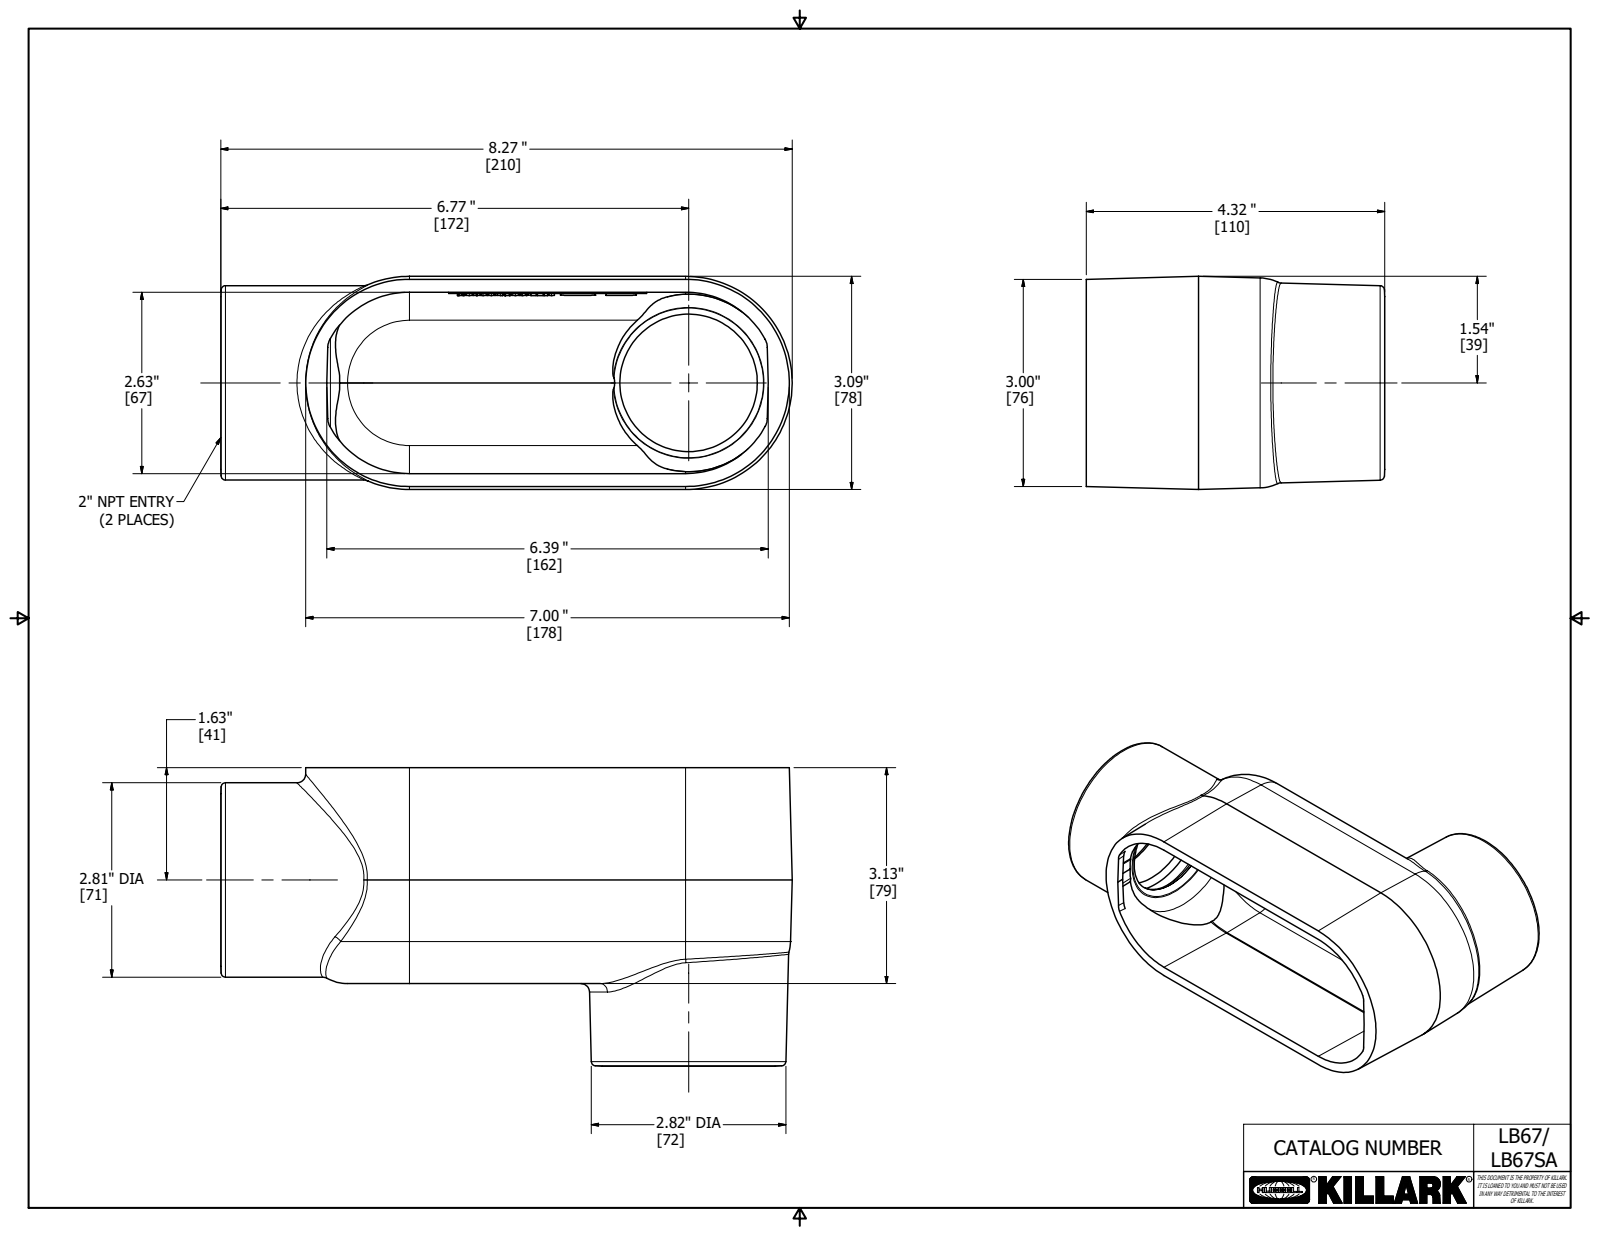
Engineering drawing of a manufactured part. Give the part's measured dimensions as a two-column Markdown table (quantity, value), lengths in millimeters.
| quantity | value |
| --- | --- |
| part name | 17708-2 |
| STEP written by | Autodesk Inventor 2018 (AUTOMOTIVE_DESIGN) |
| units | millimeters |
| bodies | 1 solid, 879 faces (531 planar, 33 cylindrical, 315 other) |
| overall size | 210.2 × 109.8 × 78.4 |
| volume | 279 100 mm³ |
| surface area | 108 500 mm² |
| round holes (diameter × count) | 60.5 × 2, 1.2 × 1, 10.3 × 1, 65.9 × 1 |
| round bosses / shafts (diameter × count) | 71.5 × 1, 12.7 × 1, 1.4 × 1 |
| partial cylindrical surfaces (radius × count) | 3.2 × 4, 11.1 × 2, 12.7 × 2, 15.9 × 2, 0.2 × 1, 0.2 × 1, 0.4 × 1, 1.6 × 1 |
| main face-to-face distances | 4.7, 73.6, 78.4, 68.8, 79.4, 5.6, 72.8, 68, 0.8, 0.8 |
| hole center spacings | 3.1 |
